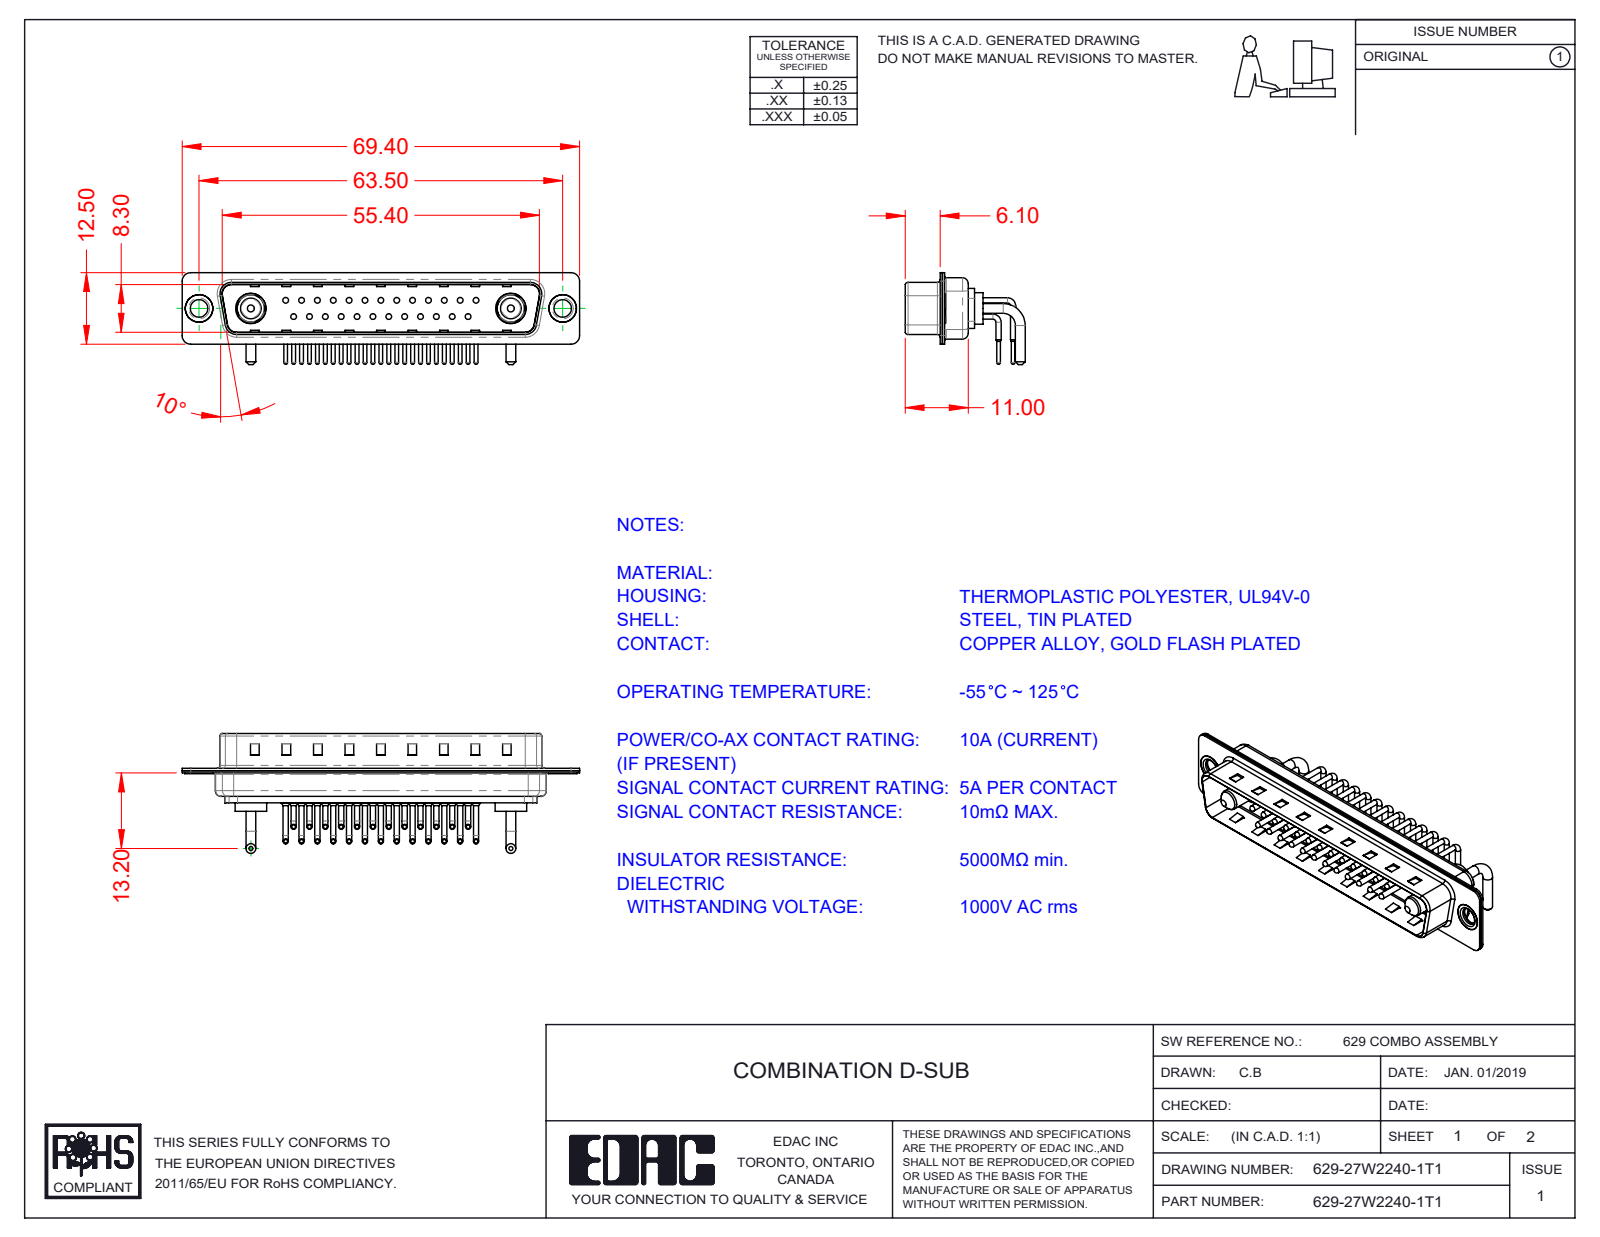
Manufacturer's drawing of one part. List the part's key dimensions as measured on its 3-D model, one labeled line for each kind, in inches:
Part name (STEP PRODUCT): 629Combo Thru Hole Rivet; 629Combo Housing_27W2; 629Combo Contact Row 2; Power Pin_10A RA (+4 more)
STEP written by: SolidWorks 2020 (CONFIG_CONTROL_DESIGN)
Units: inches
Bodies: 34 solids, 3222 faces (1823 planar, 1067 cylindrical, 332 other)
Overall size (bounding box): 2.732 × 0.825 × 0.632
Volume: 0.247 in³ · Surface area: 15.27 in²
Round holes (diameter × count): ⌀0.03 ×25, ⌀0.063 ×25, ⌀0.079 ×25, ⌀0.12 ×2, ⌀0.157 ×2, ⌀0.189 ×2, ⌀0.191 ×2, ⌀0.209 ×2
Round bosses / shafts (diameter × count): ⌀0.035 ×50, ⌀0.059 ×25, ⌀0.039 ×25, ⌀0.026 ×25, ⌀0.067 ×4, ⌀0.217 ×2, ⌀0.205 ×2, ⌀0.197 ×2
Partial cylindrical surfaces — rounded edges, fillets, slot ends (radius × count): R0.04 ×25, R0.059 ×16, R0.079 ×12, R0.02 ×8, R0.063 ×8, R0.01 ×4, R0.024 ×4, R0.026 ×4
Main face-to-face distances: 0.016, 0.031, 0.374, 0.358, 0.343, 0.39, 0.22, 0.03, 0.047, 0.014
Hole centre spacings: 0.124, 0.109, 0.218, 0.327, 0.198, 0.294, 0.436, 0.198
